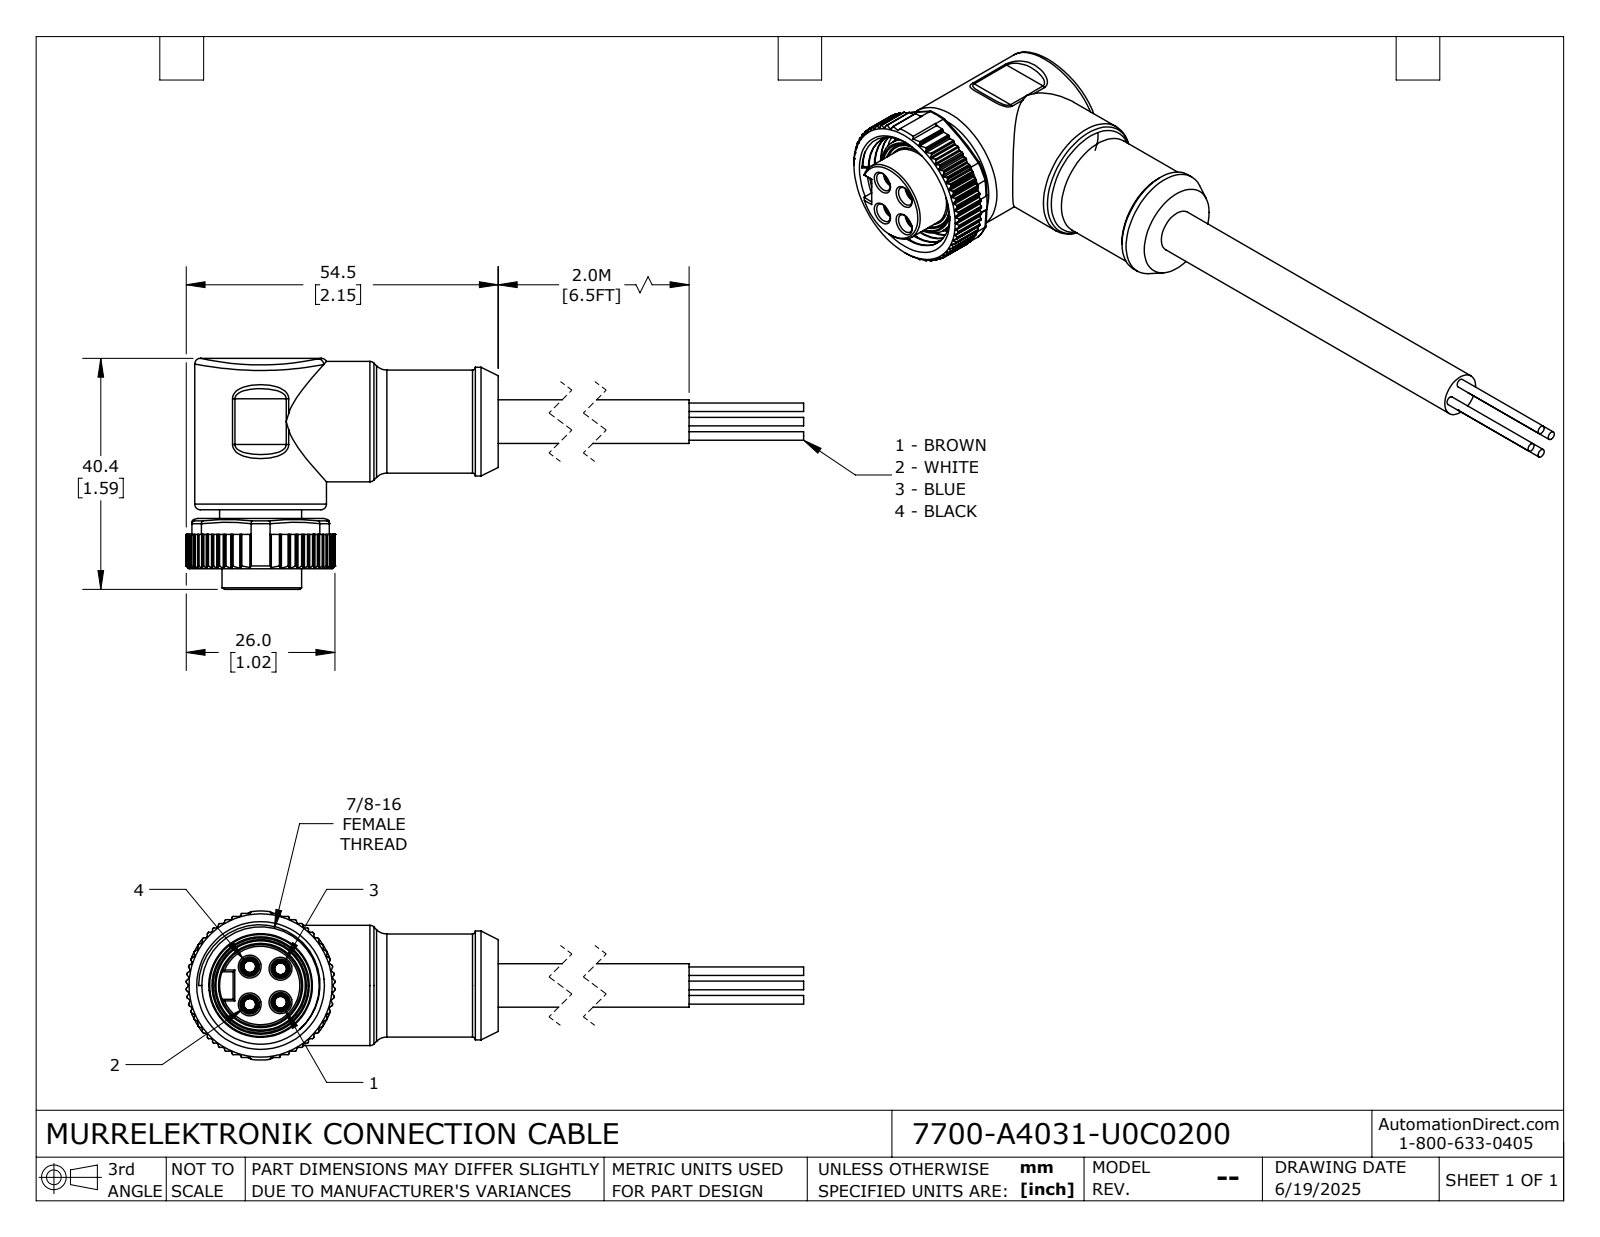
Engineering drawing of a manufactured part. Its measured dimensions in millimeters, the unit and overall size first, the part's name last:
Units: millimetres
Overall size (bounding box): 144.49 × 40.36 × 26
Round holes (diameter × count): ⌀2.05 ×4, ⌀3 ×4, ⌀3.4 ×4, ⌀15.5 ×1, ⌀15.6 ×1, ⌀20.5 ×1, ⌀22.23 ×1
Round bosses / shafts (diameter × count): ⌀1.5 ×4, ⌀23 ×1, ⌀21 ×1, ⌀19 ×1, ⌀18.1 ×1, ⌀18 ×1, ⌀17.8 ×1, ⌀14.3 ×1
Partial cylindrical surfaces — rounded edges, fillets, slot ends (radius × count): R0.2 ×126, R0.3 ×16, R0.1 ×4, R0.73 ×4, R1 ×4, R2.5 ×4, R13 ×1, R50 ×1
Main face-to-face distances: 1.5, 3.6, 8.8, 10.3, 12.4, 13.9, 7.3, 3, 10.9, 21
Hole centre spacings: 3.81, 4.54, 5.39, 8.22, 5.84, 6.6
Volume: 26 793 mm³ · Surface area: 9 847 mm²
Bodies: 1 solid, 700 faces (294 planar, 315 cylindrical, 91 other)
Part name (STEP PRODUCT): 7700-A4031-U0C0200
STEP written by: SolidWorks 2024 (CONFIG_CONTROL_DESIGN)
